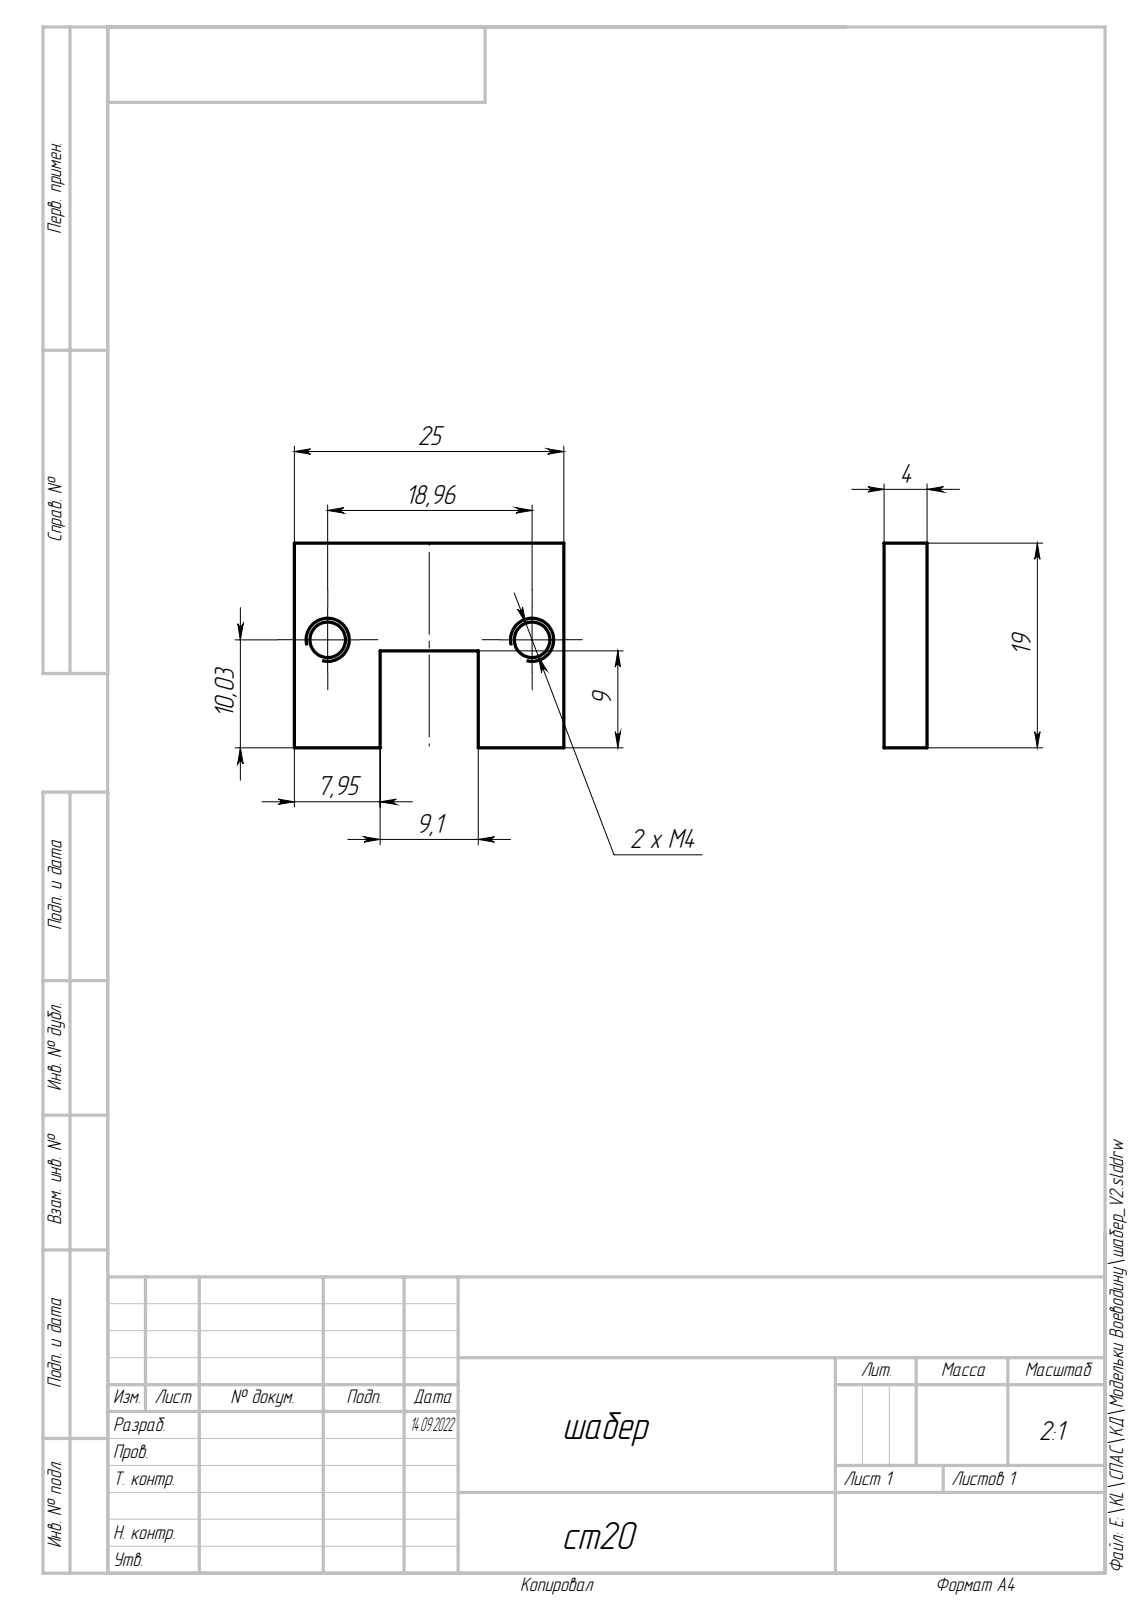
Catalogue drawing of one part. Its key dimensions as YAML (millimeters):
part_name: "шабер"
step_written_by: "SolidWorks 2021 (AUTOMOTIVE_DESIGN)"
units: millimeters
bodies: {solids: 1, faces: 14, planar: 10, cylindrical: 4, other: 0}
overall_size: [25, 19, 4]
volume: 1504
surface_area: 1259
round_holes:
  - {diameter: 3.3, count: 2}
face_to_face_distances: [4, 25, 7.95, 17.05, 19, 9, 10, 9.1]
hole_center_spacings: [18.96]
